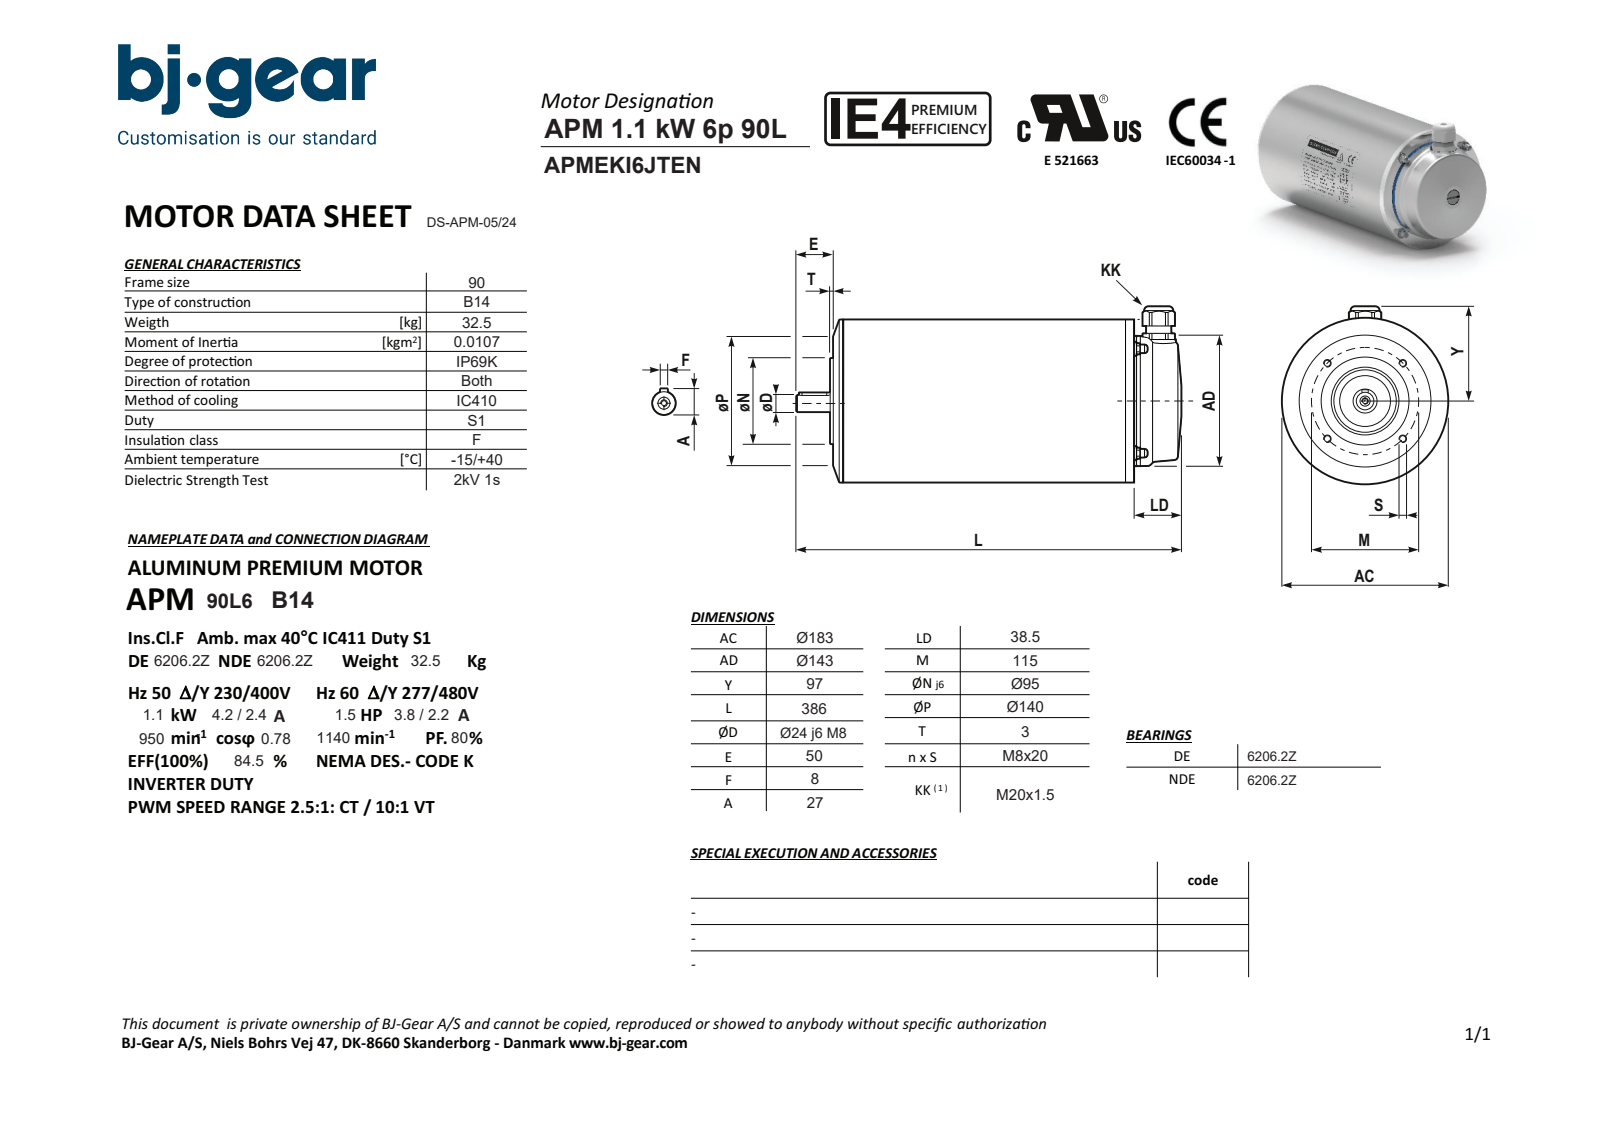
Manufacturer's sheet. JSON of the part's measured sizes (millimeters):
{"part_name": "APMEKI6JTENN4KCR2-N---NNN", "step_written_by": "Solid Edge (AUTOMOTIVE_DESIGN)", "units": "millimeters", "bodies": {"solids": 1, "faces": 156, "planar": 75, "cylindrical": 50, "other": 31}, "overall_size": [386, 187.3, 182.6], "volume_mm3": 8327000, "surface_area_mm2": 247972, "round_holes": [[6.65, 5], [8.4, 1], [16, 1], [28, 1], [82, 1]], "round_bosses_or_shafts": [[11.5, 4], [7, 4], [182.6, 1], [182.6, 1], [143, 1], [95, 1], [30, 1], [24, 1]], "partial_cylinders_radius": [[4, 2], [13.2, 1]], "face_to_face_distances": [297.5, 6, 291.5, 3, 9, 300.5, 8, 336, 38.5, 330], "hole_center_spacings": [57.5, 81.32, 115]}
